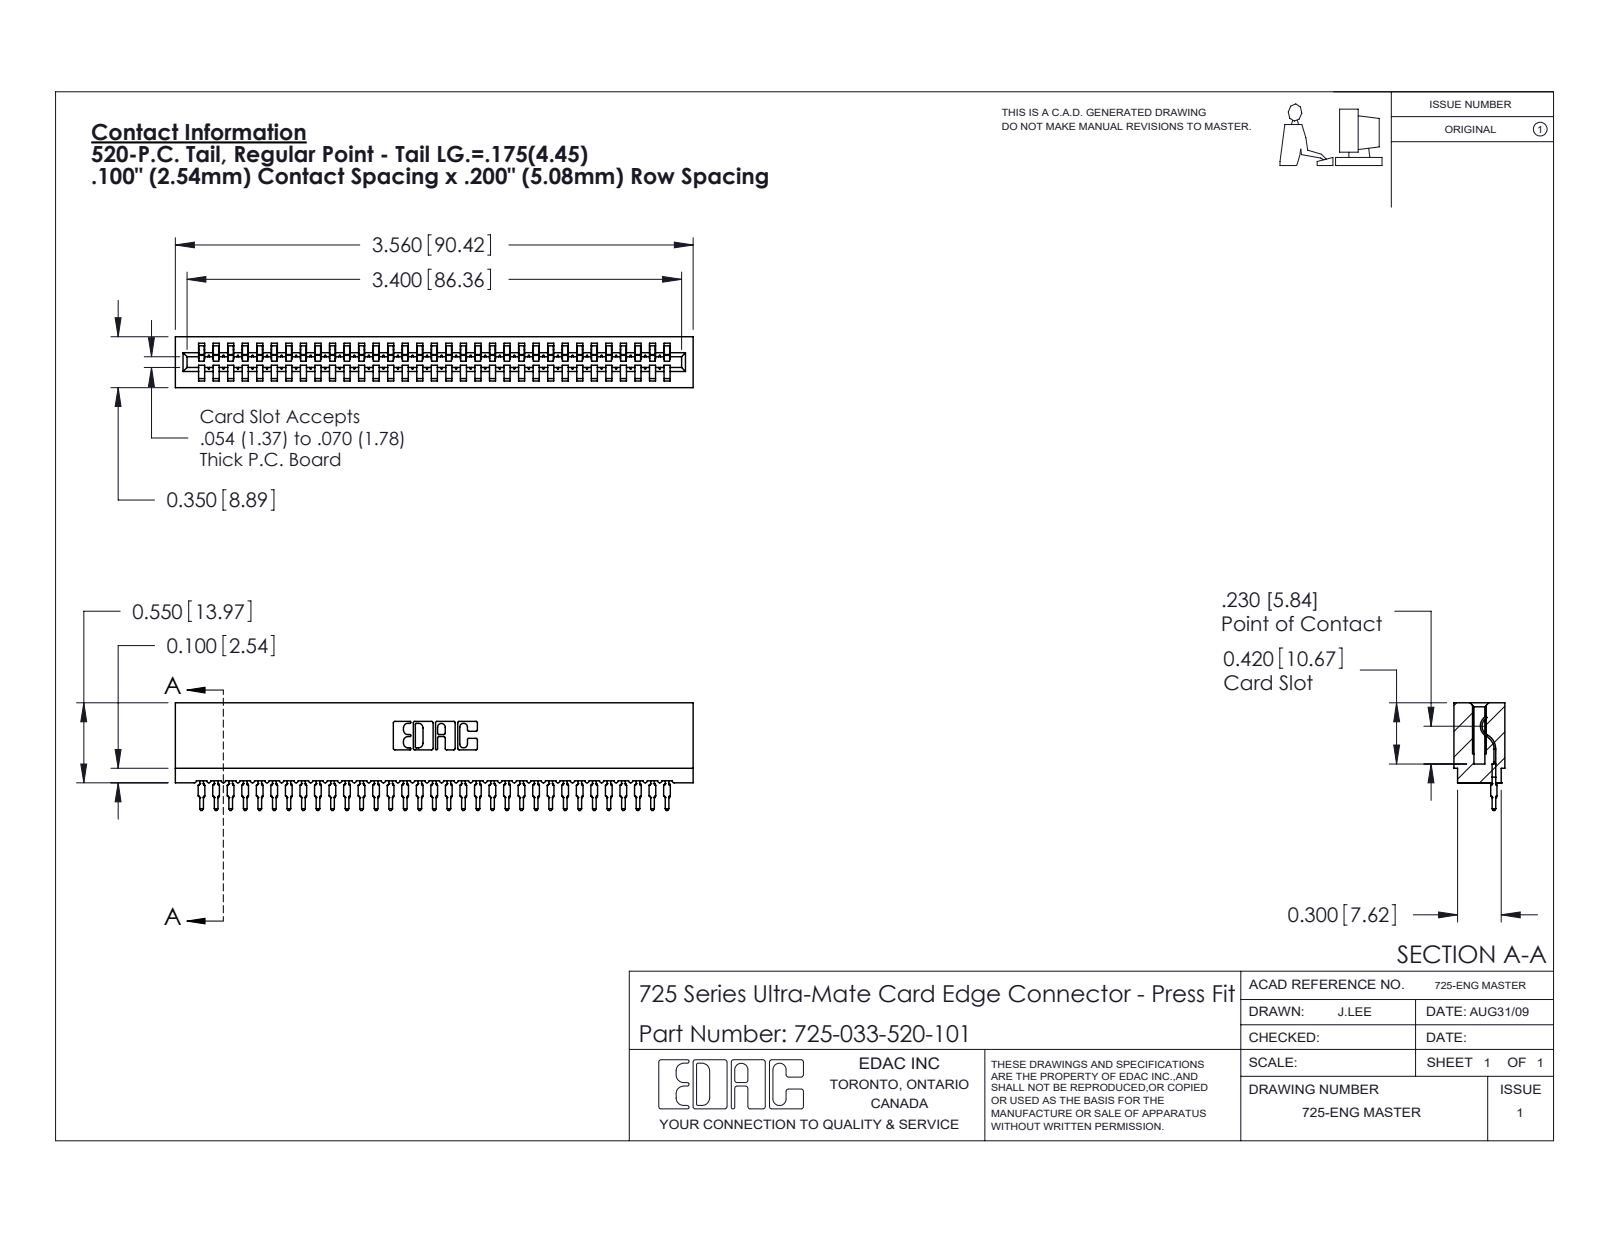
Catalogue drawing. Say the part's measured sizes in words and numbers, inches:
The part is named "745-292-001_520; 725-033-520-101; 725 Part_Insulator Option - 01". Its 3-D file was written by "SolidWorks 2020 (CONFIG_CONTROL_DESIGN)". It is 34 solids with 3791 faces: 2266 planar, 667 cylindrical and 858 other. Overall it measures 3.56 by 0.741 by 0.35 inches. Its volume is 0.419 cubic inches and its surface area 19.94 square inches. Partial cylindrical surfaces (rounded edges, fillets, slot ends): 66 of radius 0.015, 66 of radius 0.021, 22 of radius 0.01, 6 of radius 0.007, 6 of radius 0.031, 4 of radius 0.005, 4 of radius 0.011, 3 of radius 0.026. The main face-to-face distances are 0.2, 0.1, 0.35, 0.3, 0.212, 0.138, 0.4, 0.5, 0.045, 0.305.
